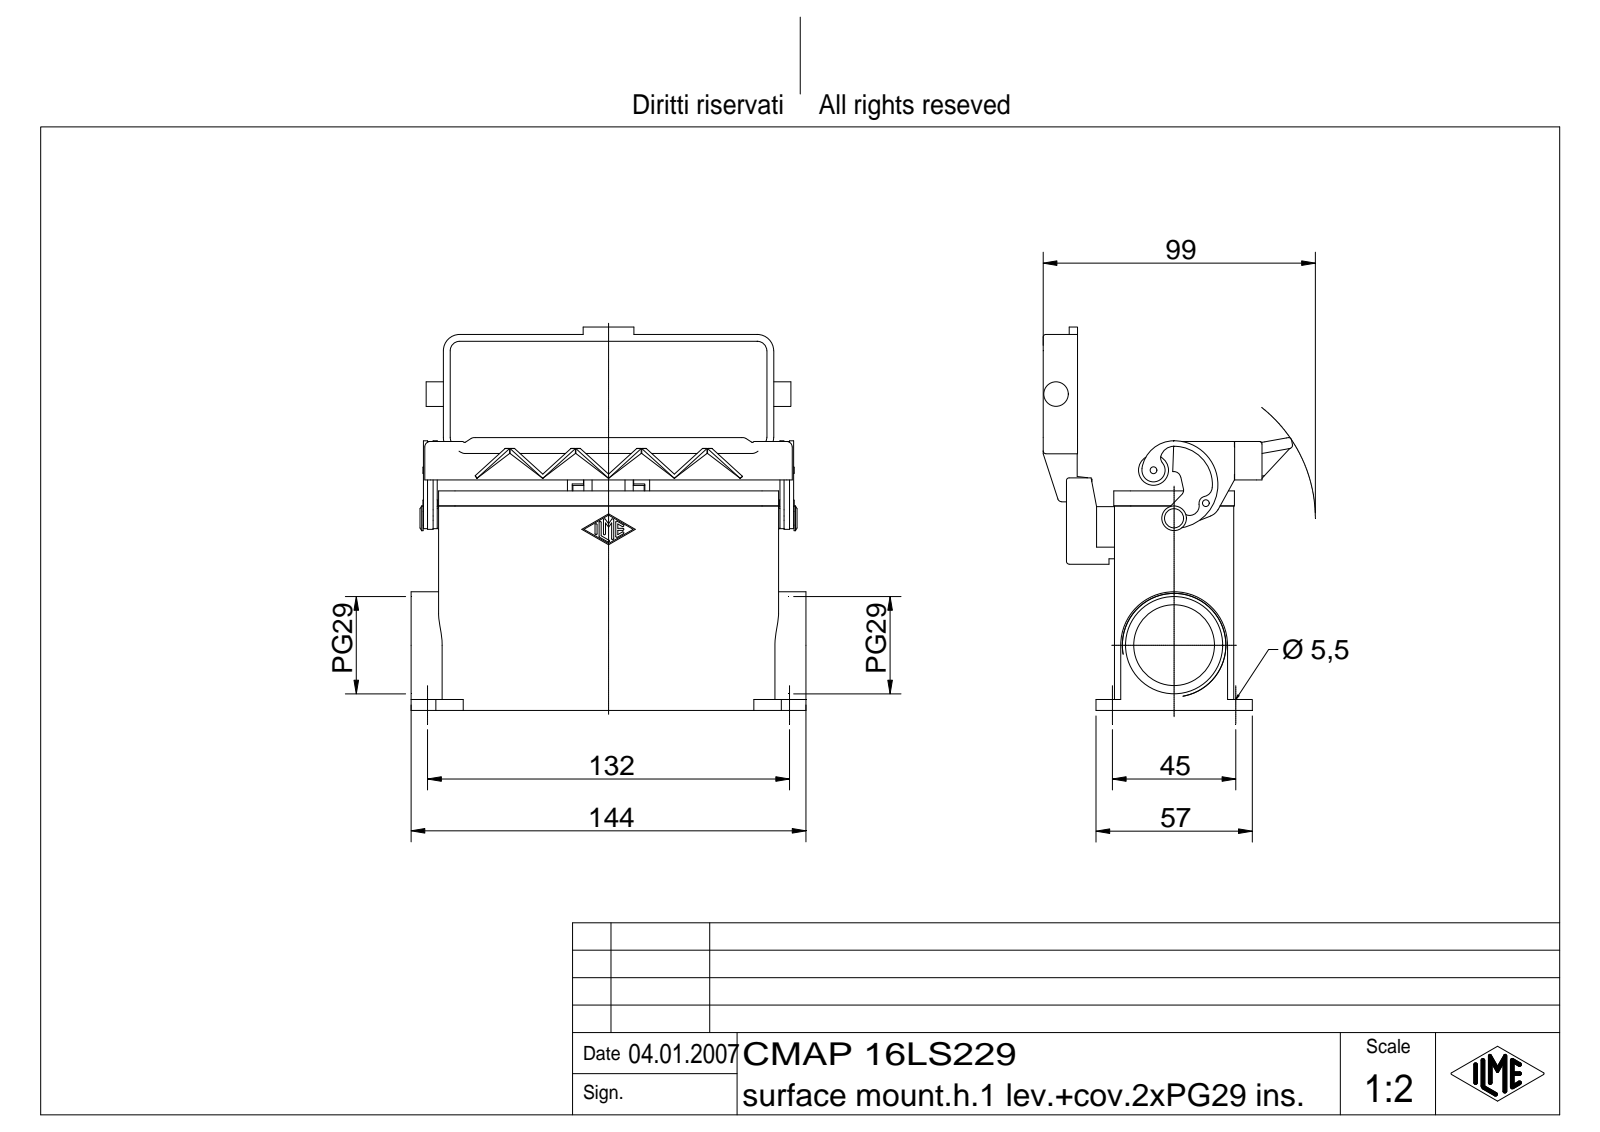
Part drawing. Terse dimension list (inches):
name: CMAP 16LS229
written by: Autodesk Inventor 7 (AUTOMOTIVE_DESIGN)
unit: in
bodies: 6 solids, 628 faces (282 planar, 182 cylindrical, 164 other)
size: 5.669 × 5.5 × 3.581
volume: 11.31 in³; area: 164.3 in²
holes: 4× ⌀0.217, 1× ⌀0.079, 1× ⌀0.157, 1× ⌀1.161, 1× ⌀1.397
bosses: 2× ⌀0.354, 2× ⌀0.197, 1× ⌀0.433, 1× ⌀0.276, 1× ⌀0.157, 1× ⌀0.118, 1× ⌀0.098
rounds: 18× R0.039, 14× R0.015, 12× R0.079, 12× R0.236, 6× R0.059, 6× R0.138, 4× R0.118, 3× R0.02
face distances: 0.118, 1.594, 1.713, 0.157, 1.476, 1.024, 2.618, 2.736, 1.142, 1.004
hole spacings: 1.772, 5.197, 5.491, 2.088
